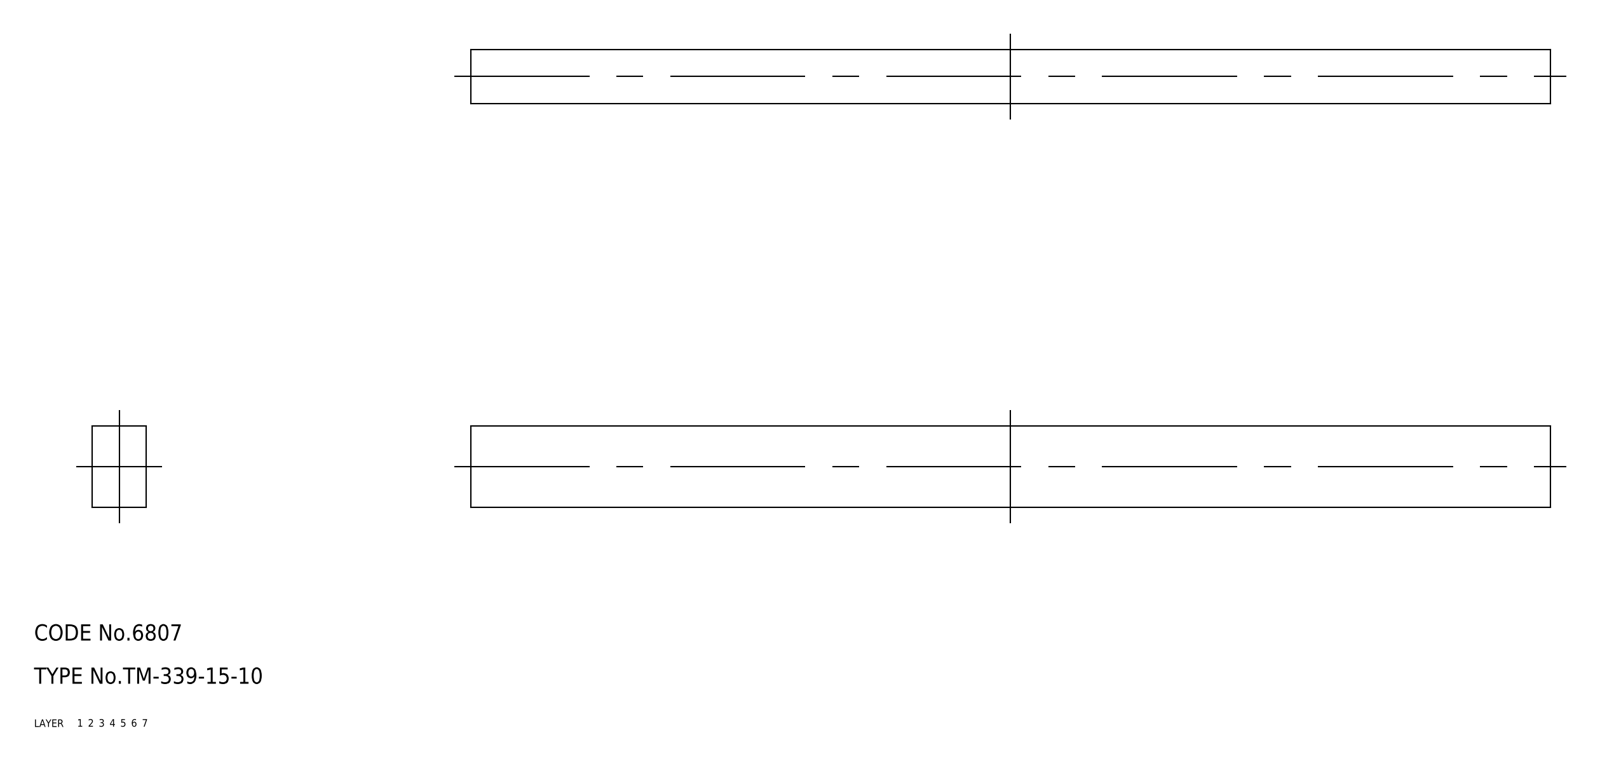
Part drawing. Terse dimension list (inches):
name: rubber foam; TM_339_15_10
written by: SolidWorks 2015 (AUTOMOTIVE_DESIGN)
unit: in
bodies: 1 solid, 6 faces (6 planar, 0 cylindrical, 0 other)
size: 7.874 × 0.591 × 0.394
volume: 1.831 in³; area: 15.97 in²
face distances: 0.394, 0.591, 7.874
